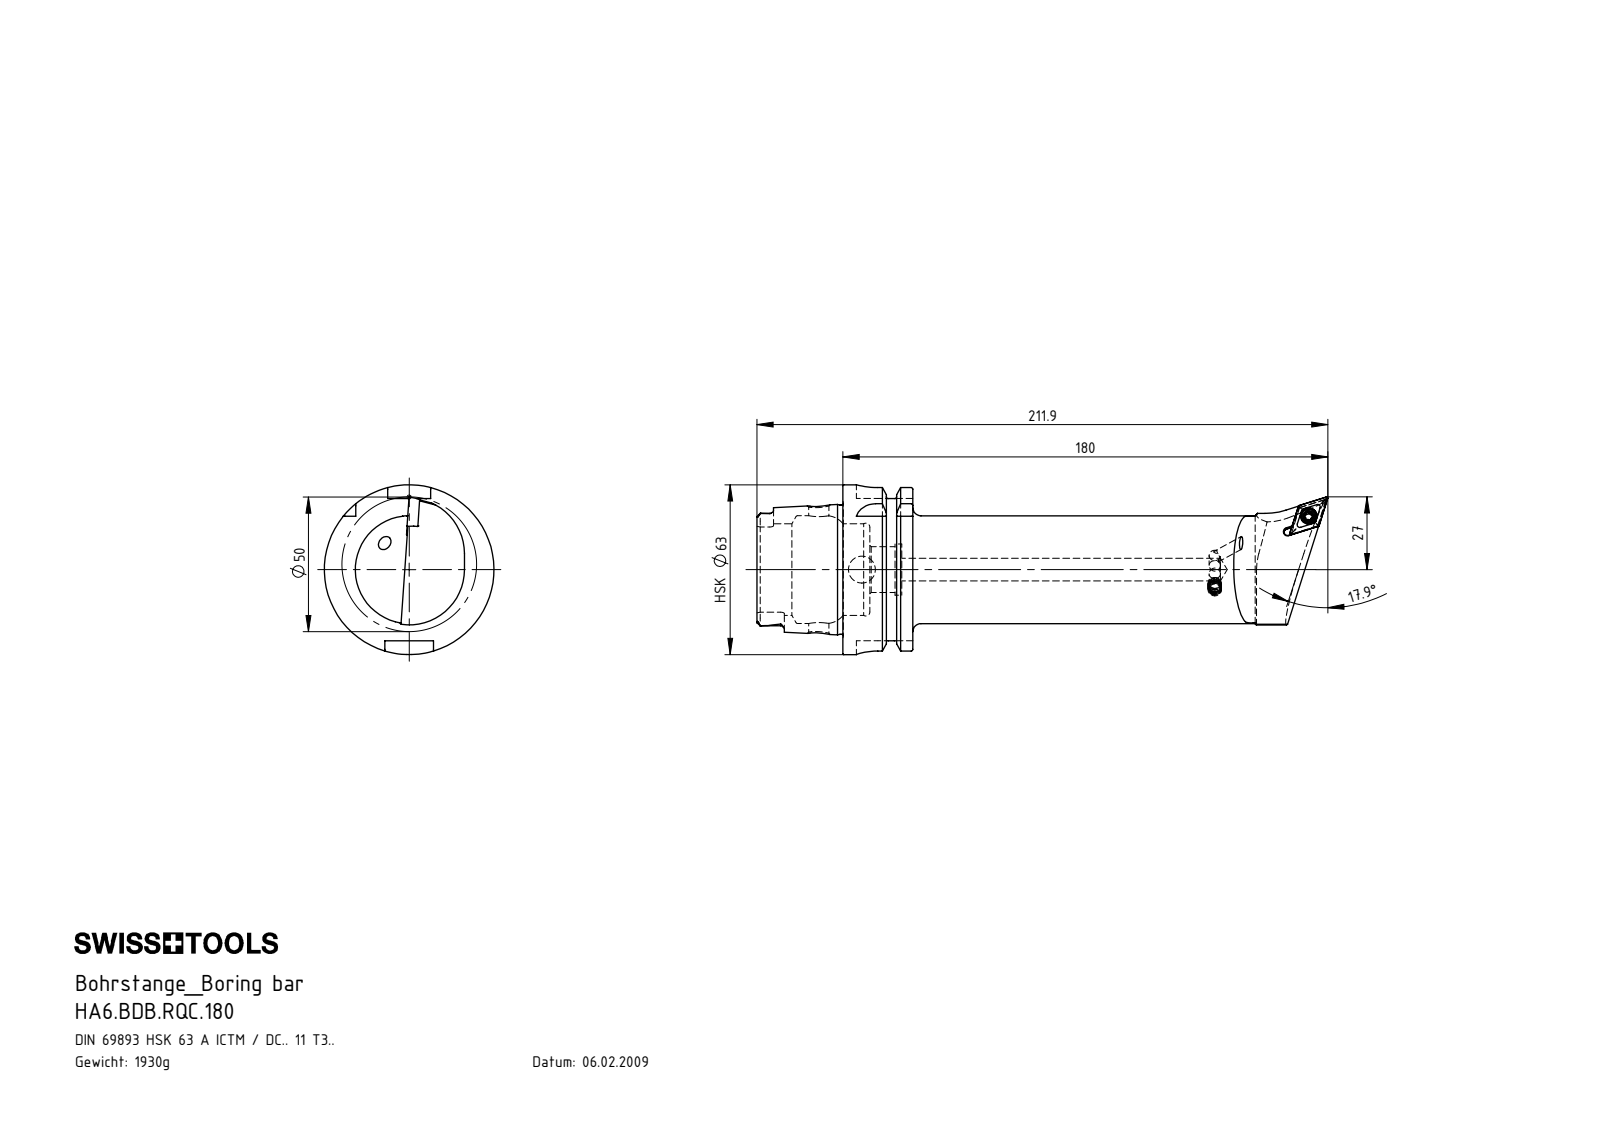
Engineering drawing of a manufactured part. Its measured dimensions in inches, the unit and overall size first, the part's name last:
Units: inches
Overall size (bounding box): 8.343 × 2.48 × 2.48
Round holes (diameter × count): ⌀0.165 ×2, ⌀0.13 ×1, ⌀0.157 ×1, ⌀0.173 ×1, ⌀0.197 ×1, ⌀0.24 ×1, ⌀0.295 ×1, ⌀0.331 ×1, ⌀0.394 ×1, ⌀0.669 ×1, ⌀0.748 ×1, ⌀1.339 ×1
Round bosses / shafts (diameter × count): ⌀2.48 ×1, ⌀2.163 ×1, ⌀1.887 ×1, ⌀0.207 ×1, ⌀0.197 ×1, ⌀0.157 ×1
Partial cylindrical surfaces — rounded edges, fillets, slot ends (radius × count): R0.013 ×6, R0.023 ×6, R0.055 ×6, R0.315 ×4, R0.111 ×2, R0.113 ×2, R0.049 ×1, R0.236 ×1
Main face-to-face distances: 1.022, 0.63, 0.392, 1.256, 1.648, 2.278, 2.079, 0.858, 0.467, 2.114
Volume: 14.9 in³ · Surface area: 68.89 in²
Bodies: 5 solids, 306 faces (76 planar, 90 cylindrical, 140 other)
Part name (STEP PRODUCT): HA6-BDB.RQC.180; KVT_MB_600_050; WCB-ER2.001.009_A; DCMT11T304 (+1 more)
STEP written by: SolidWorks 2012 (CONFIG_CONTROL_DESIGN)
